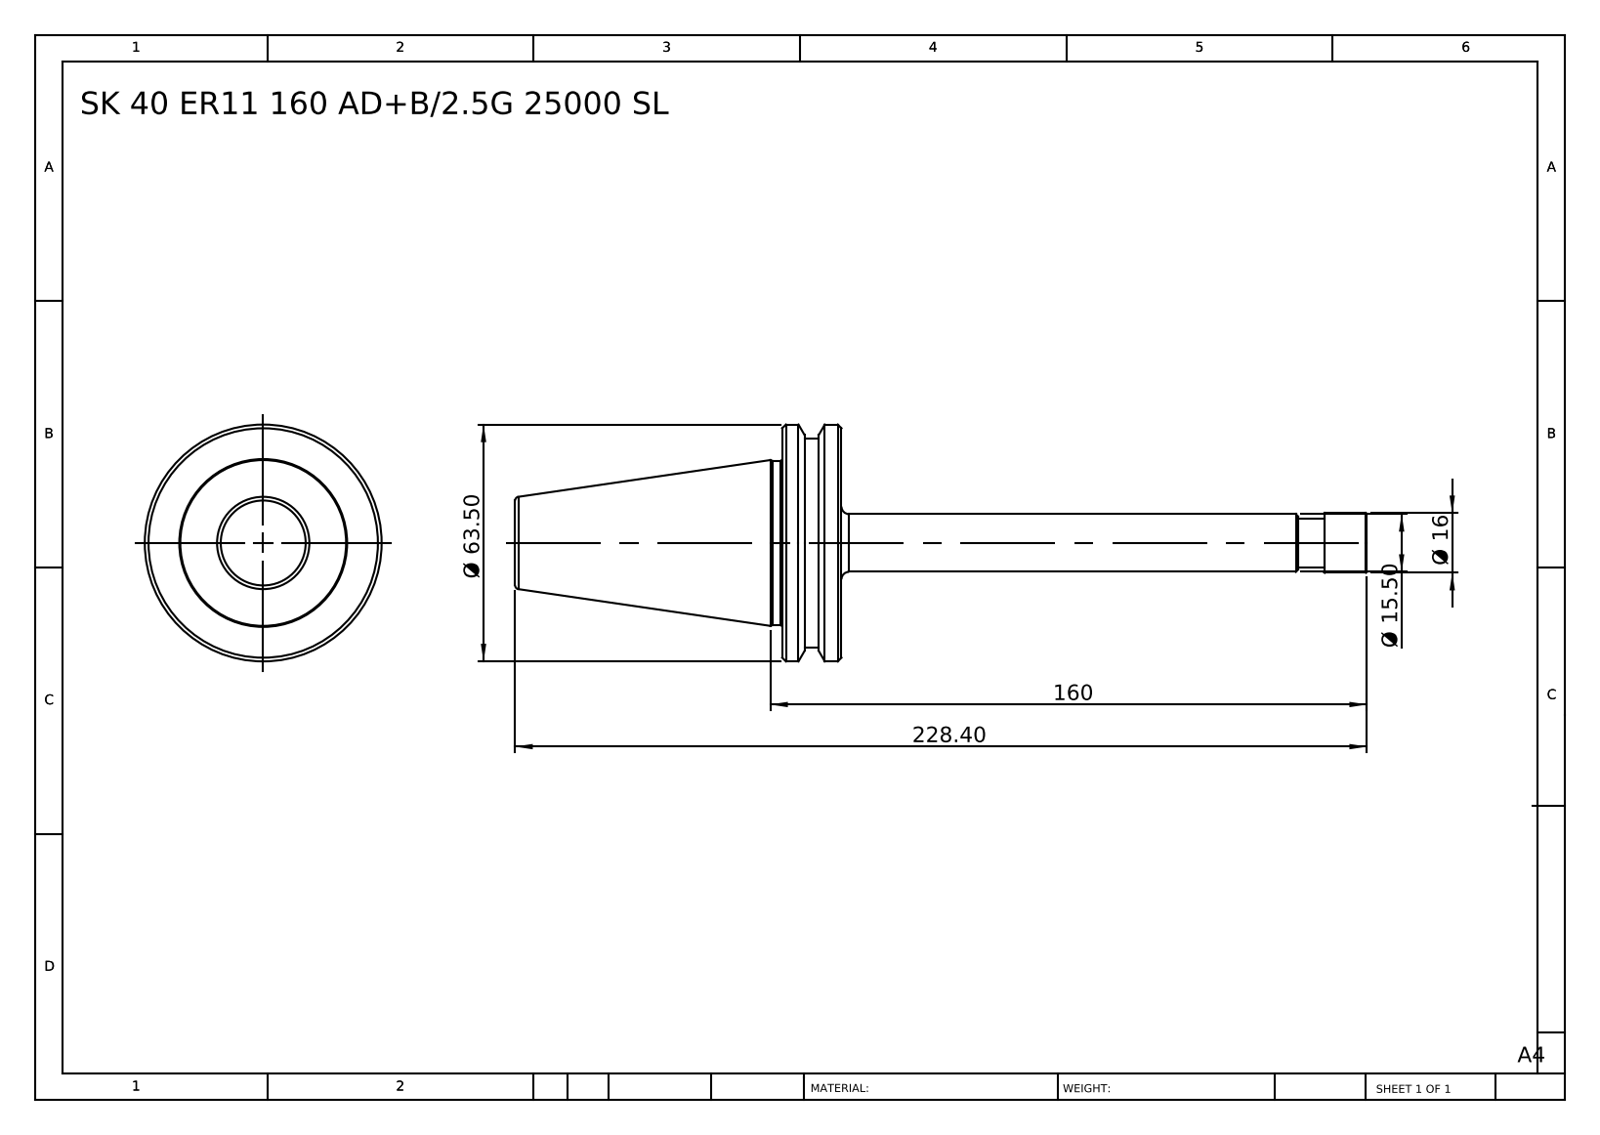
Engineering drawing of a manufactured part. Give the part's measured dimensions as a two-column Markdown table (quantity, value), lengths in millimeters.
| quantity | value |
| --- | --- |
| part name | SK 40 ER11M 160 AD+B-2.5G 25000 SL |
| STEP written by | SolidWorks 2014 (CONFIG_CONTROL_DESIGN) |
| units | millimeters |
| bodies | 1 solid, 46 faces (8 planar, 14 cylindrical, 24 other) |
| overall size | 228.4 × 63.5 × 63.5 |
| volume | 143 458 mm³ |
| surface area | 23 832 mm² |
| round bosses / shafts (diameter × count) | 63.5 × 1, 56 × 1, 44 × 1, 16 × 1, 15.5 × 1, 12.9 × 1 |
| main face-to-face distances | 15.9, 87.5, 71.6, 140.9, 156.8, 228.4, 147, 6.1, 9.8, 81.4 |
